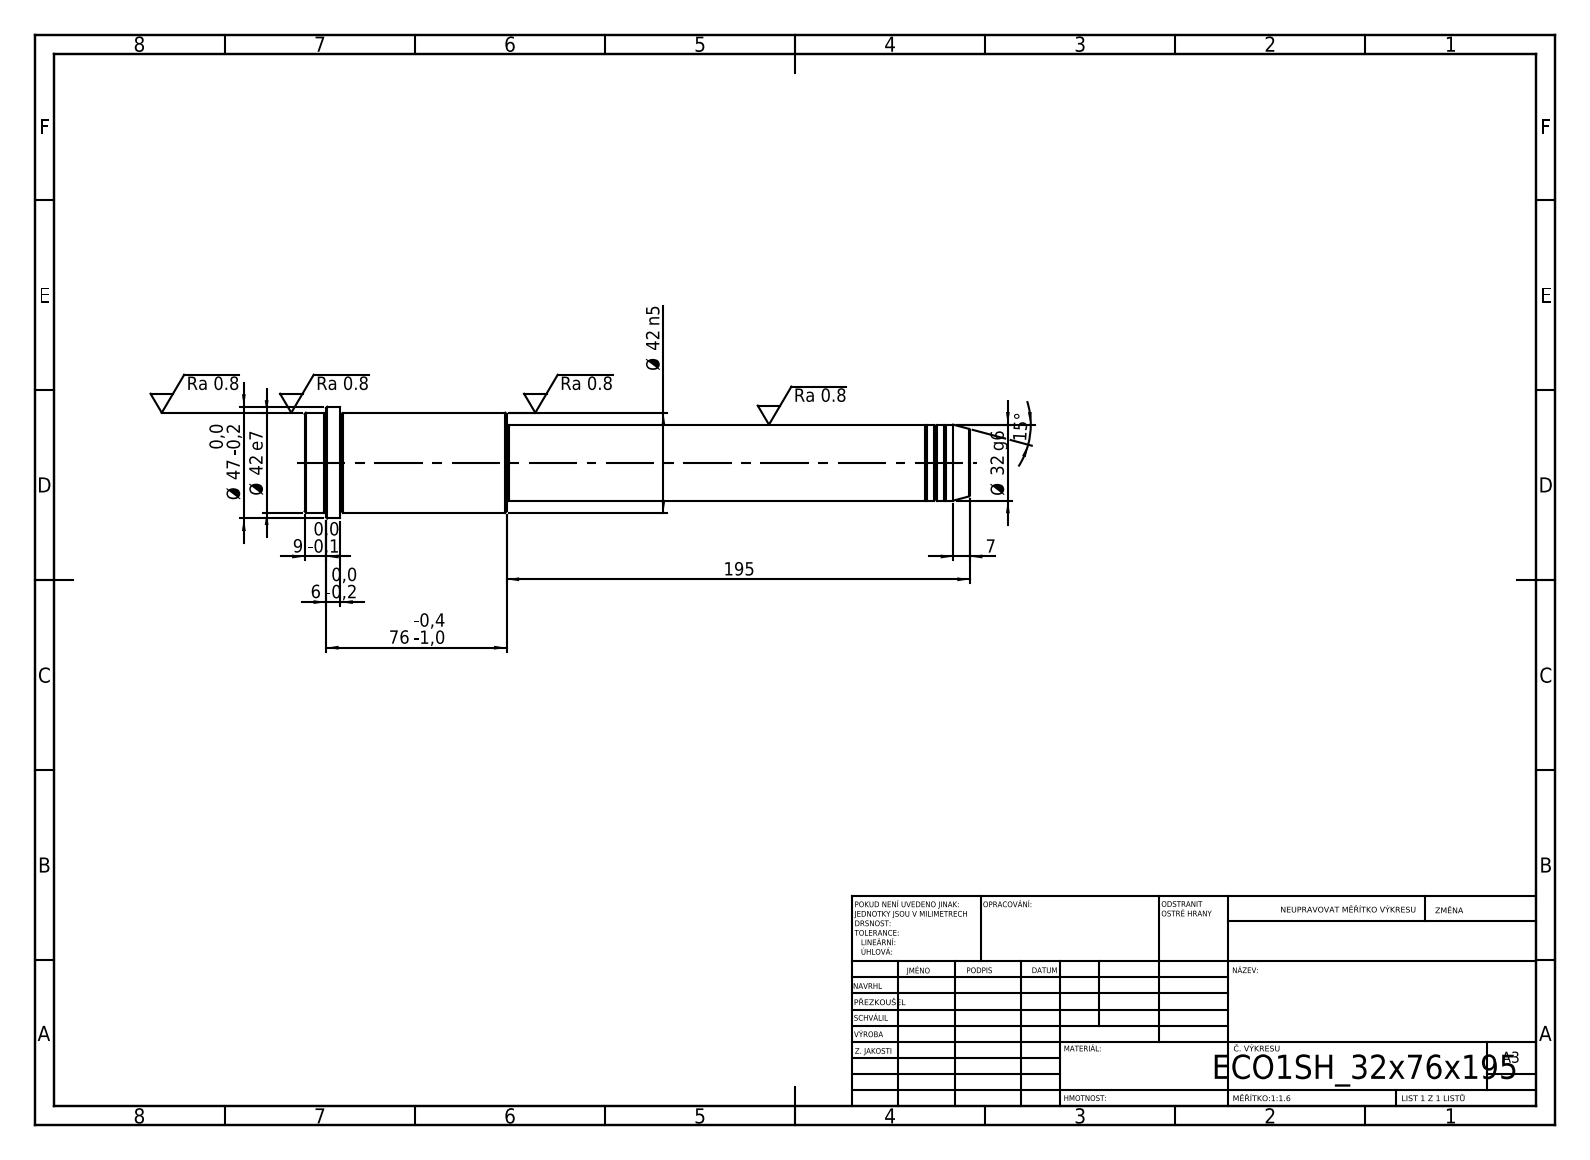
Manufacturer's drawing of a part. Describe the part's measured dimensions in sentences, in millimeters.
Its 3-D file was written by "SolidWorks 2019 (CONFIG_CONTROL_DESIGN)". It is 1 solid with 52 faces: 6 planar, 16 cylindrical and 30 other. Overall it measures 280 by 47 by 47 millimeters. Its volume is 275 731 cubic millimeters and its surface area 34 459 square millimeters. Round bosses or shafts: 1 of diameter 47, 1 of diameter 42, 1 of diameter 32, 1 of diameter 31. The main face-to-face distances are 280, 195, 85, 265, 70, 15, 271, 76, 6, 9.
